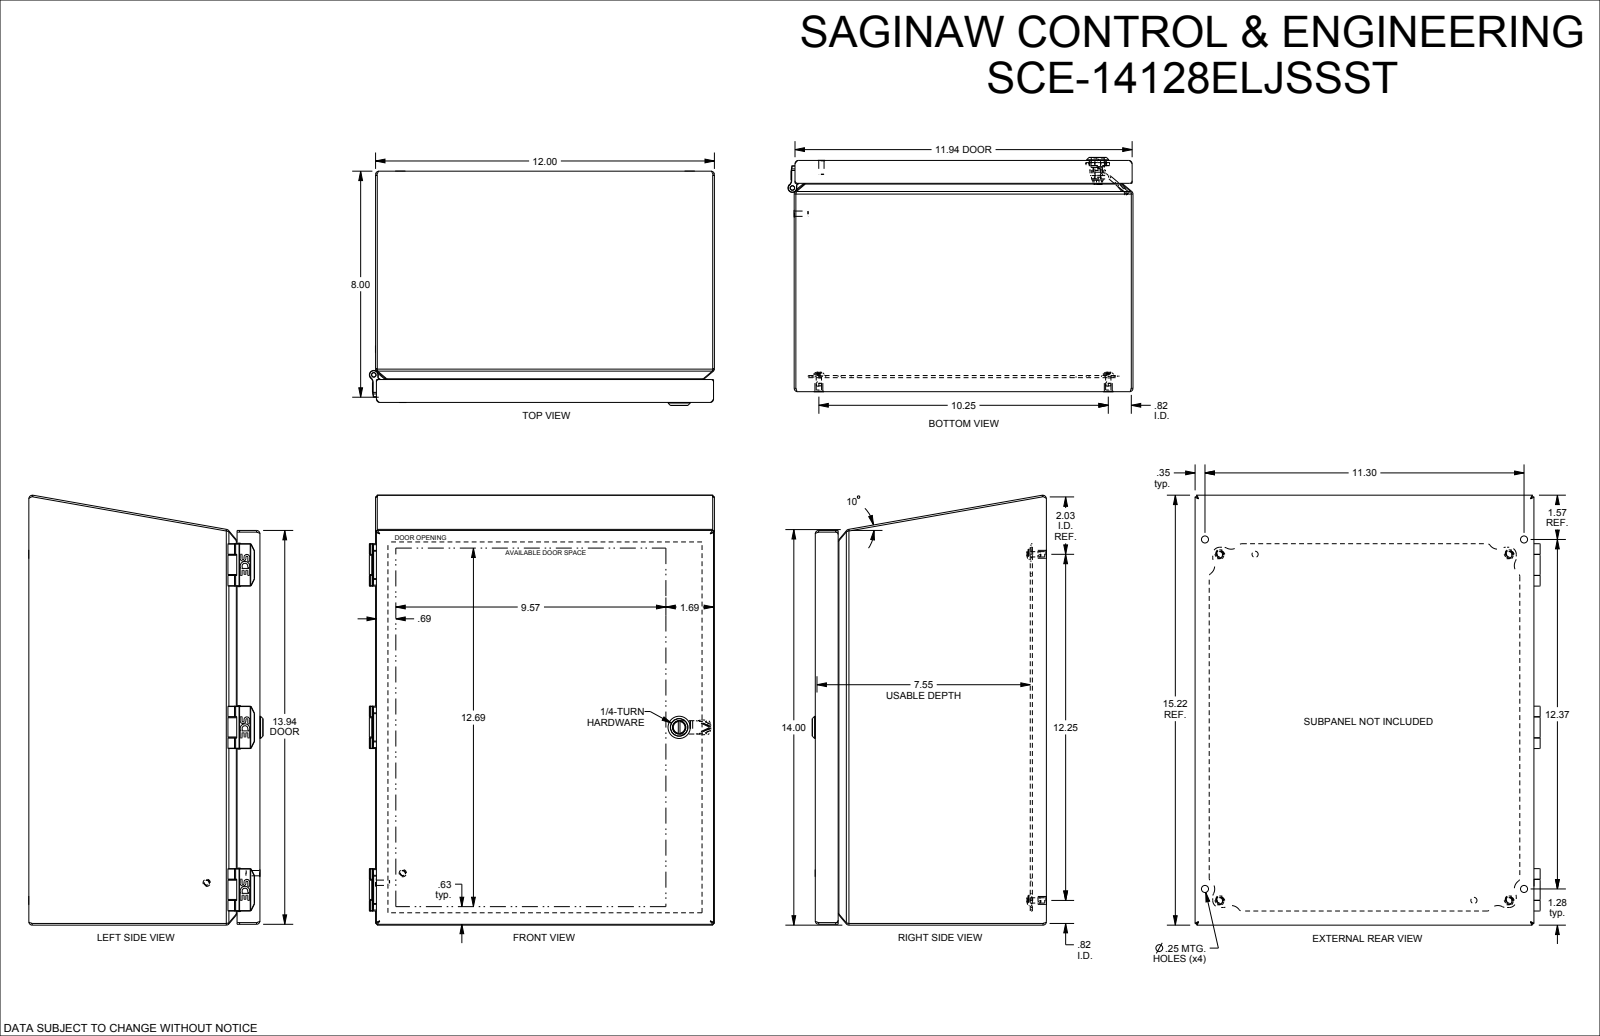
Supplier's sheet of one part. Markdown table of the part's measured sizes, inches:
| quantity | value |
| --- | --- |
| part name | SCE-14128ELJSSST |
| STEP written by | SolidWorks 2021 (AUTOMOTIVE_DESIGN) |
| units | inches |
| bodies | 41 solids, 1861 faces (711 planar, 436 cylindrical, 714 other) |
| overall size | 15.214 × 12.22 × 8.296 |
| volume | 63.23 in³ |
| surface area | 2 001 in² |
| round holes (diameter × count) | 0.16 × 6, 0.19 × 4, 0.25 × 4, 0.284 × 4, 0.02 × 3, 0.1 × 3, 0.218 × 2, 0.266 × 2, 0.158 × 1, 0.196 × 1, 0.2 × 1, 0.239 × 1 |
| round bosses / shafts (diameter × count) | 0.483 × 6, 0.237 × 6, 0.188 × 6, 0.16 × 6, 0.373 × 4, 0.28 × 4, 0.26 × 3, 0.18 × 3 |
| partial cylindrical surfaces (radius × count) | 0.03 × 62, 0.008 × 36, 0.013 × 31, 0.25 × 13, 0.01 × 12, 0.125 × 11, 0.06 × 10, 0.062 × 10 |
| main face-to-face distances | 0.059, 11.881, 0.06, 8.185, 8.126, 8.125, 8.066, 0.571, 0.512, 7.554 |
| hole center spacings | 5.75, 11.5, 15.972, 0.018, 1.25, 6.136, 9, 10.25 |
